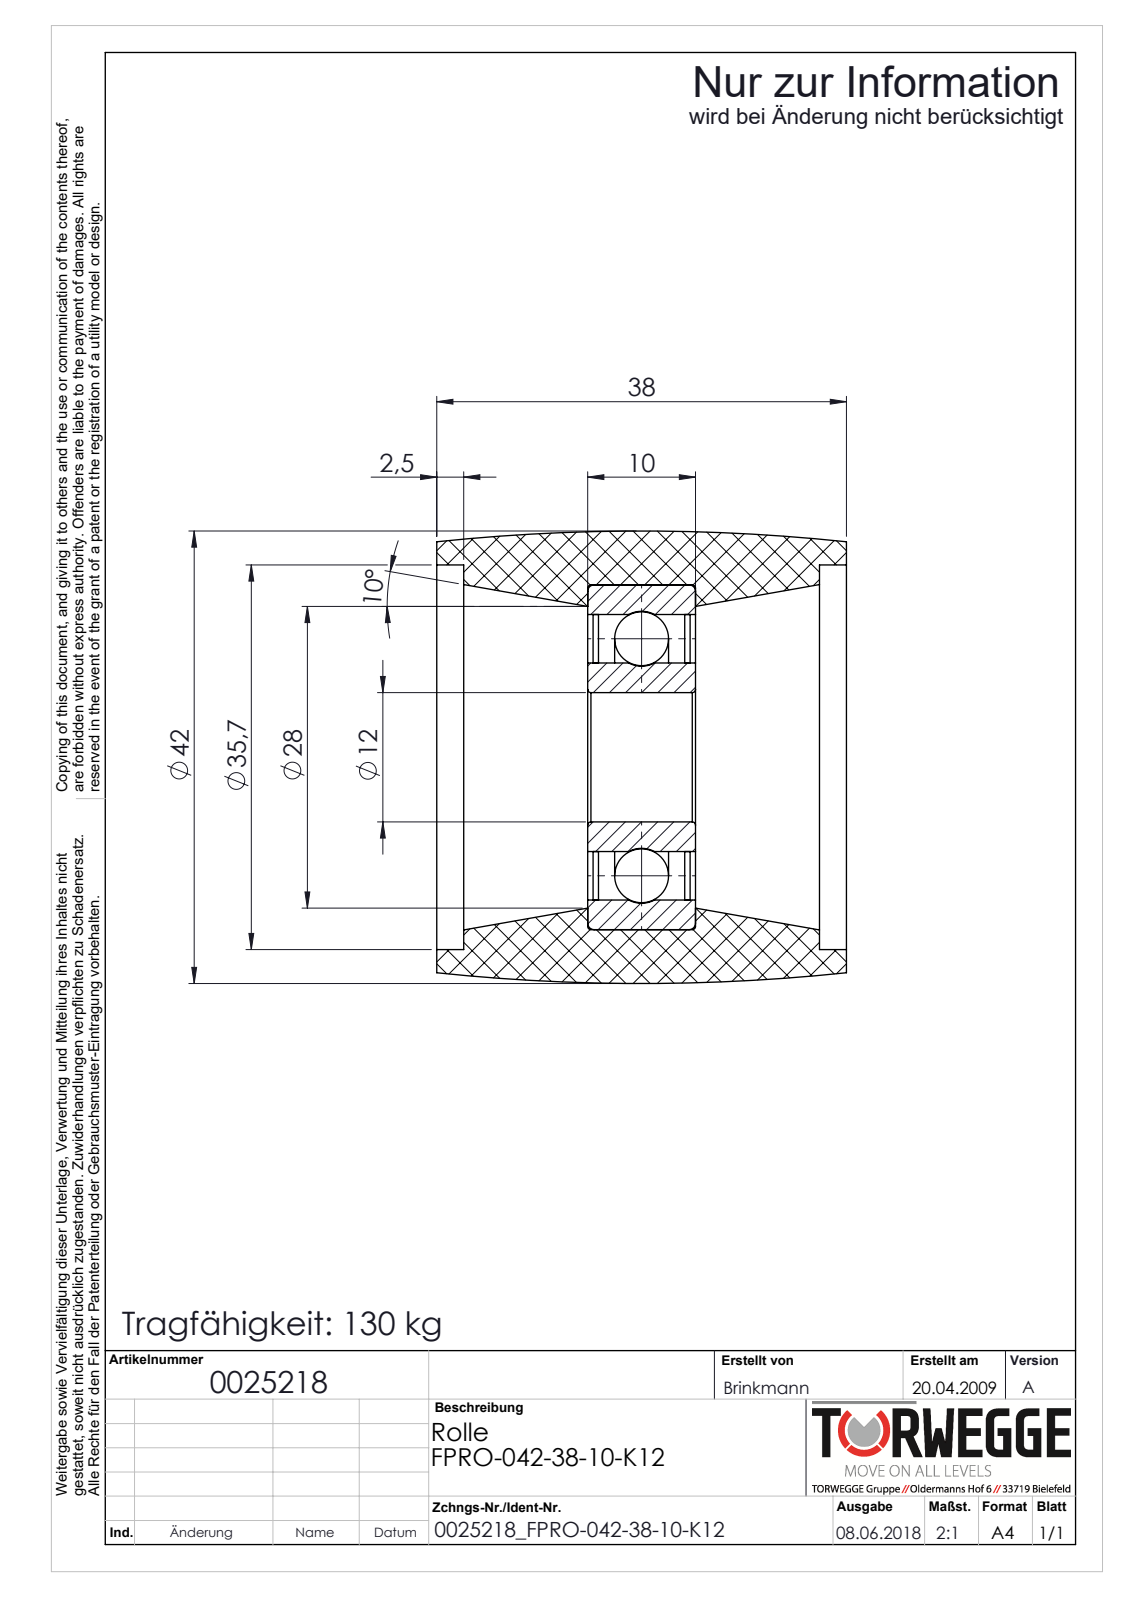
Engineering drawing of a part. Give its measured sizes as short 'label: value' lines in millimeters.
name: 0025218_FPRO-042-38-10-K12
written by: SolidWorks 2018 (AUTOMOTIVE_DESIGN)
unit: mm
bodies: 6 solids, 68 faces (14 planar, 26 cylindrical, 28 other)
size: 42 × 42 × 38
volume: 27 053 mm³; area: 15 908 mm²
holes: 1× ⌀12, 1× ⌀17.5, 1× ⌀26.5, 1× ⌀32, 1× ⌀35.7
face distances: 0.5, 9, 1, 9.5, 8.5, 14, 14.5, 15, 23, 23.5
